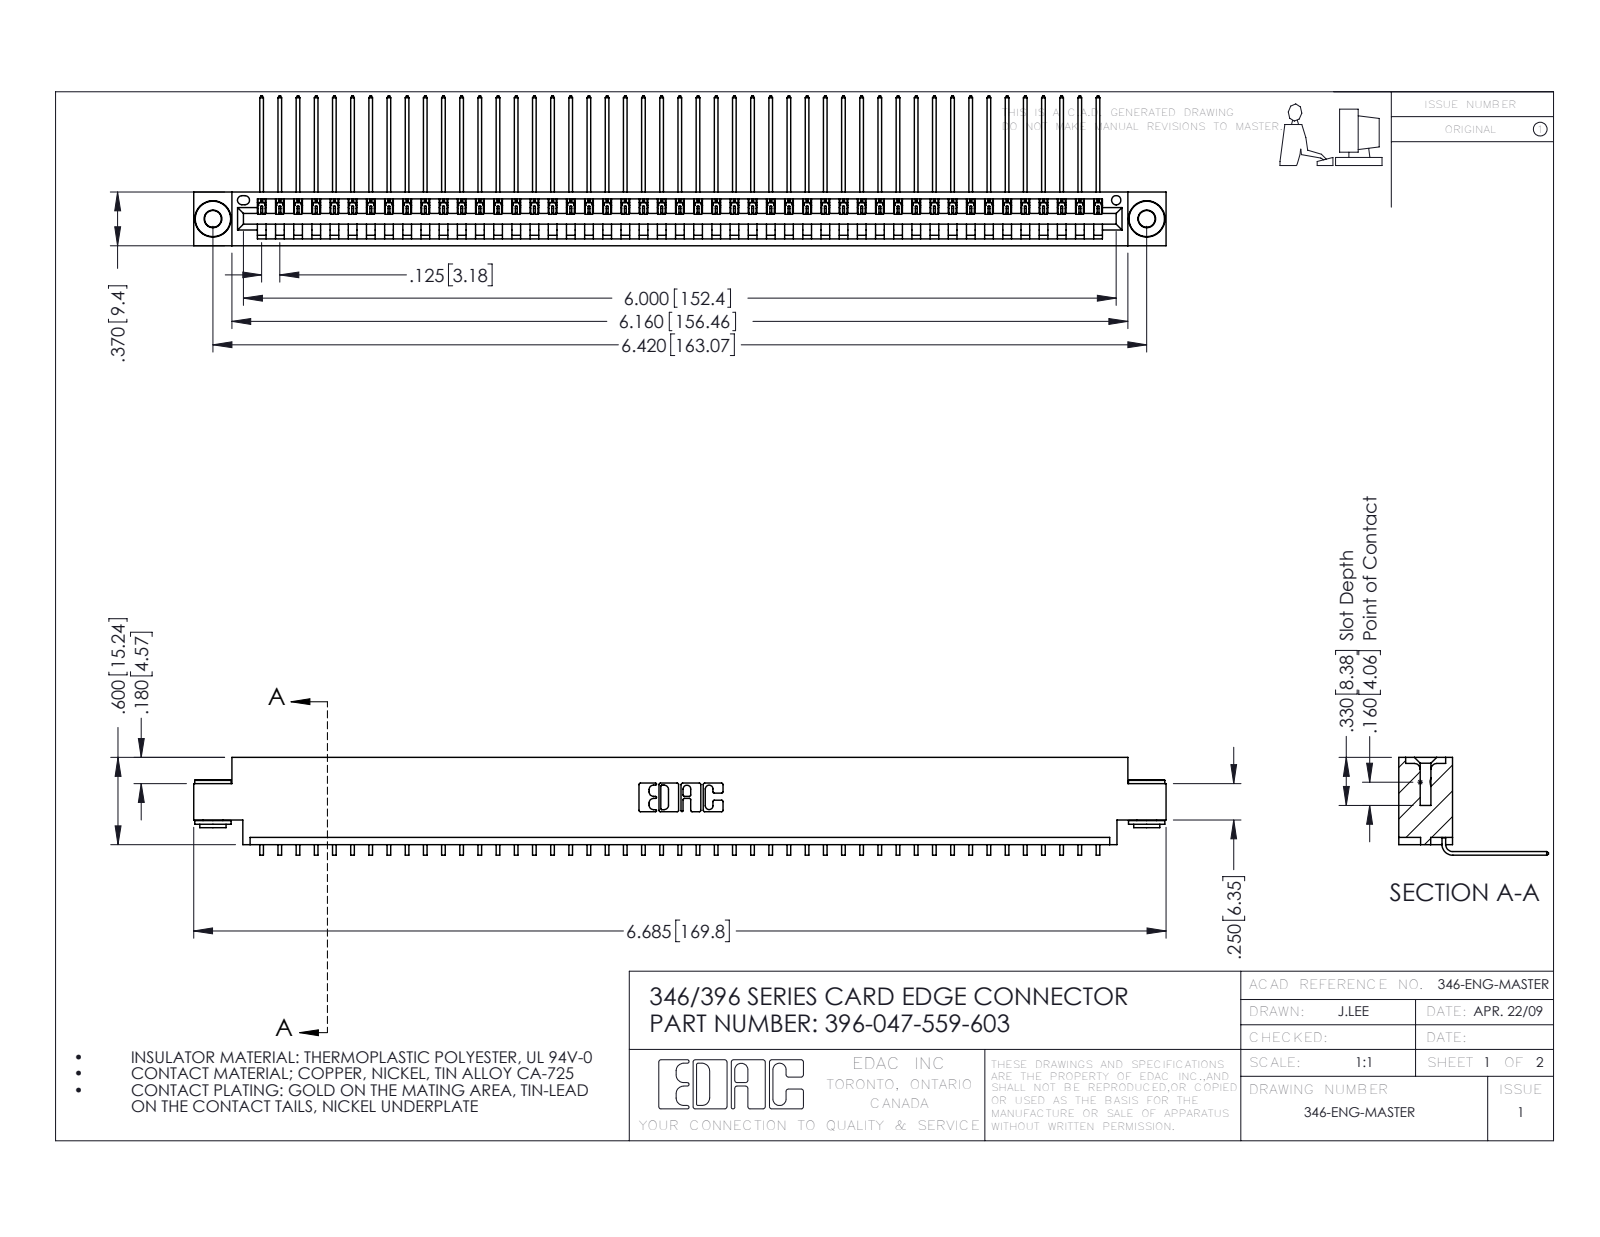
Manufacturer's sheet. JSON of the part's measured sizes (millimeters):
{"part_name": "345-250-002_345-250-002-102; 346 Part_0.170 Offset - 0.156 Dia-TH; 396-047-559-603; 345-292-001_558 559 Tail - 1", "step_written_by": "SolidWorks 2016 (CONFIG_CONTROL_DESIGN)", "units": "millimeters", "bodies": {"solids": 50, "faces": 2984, "planar": 2064, "cylindrical": 912, "other": 8}, "overall_size": [169.8, 26.2, 17.1], "volume_mm3": 16300, "surface_area_mm2": 21750, "round_holes": [[2.9, 2], [4, 2], [1.6, 1]], "round_bosses_or_shafts": [[6.4, 2], [4.6, 2], [3.5, 2]], "partial_cylinders_radius": [[0.2, 94], [0.3, 22], [0.2, 6], [0.8, 6], [0.7, 3], [0.8, 2], [1, 2], [0.4, 1]], "face_to_face_distances": [1.2, 8.2, 9.4, 0.6, 6.4, 1.8, 7.6, 3.8, 5.6, 2.5], "hole_center_spacings": [6.2, 157.8, 163.1]}
